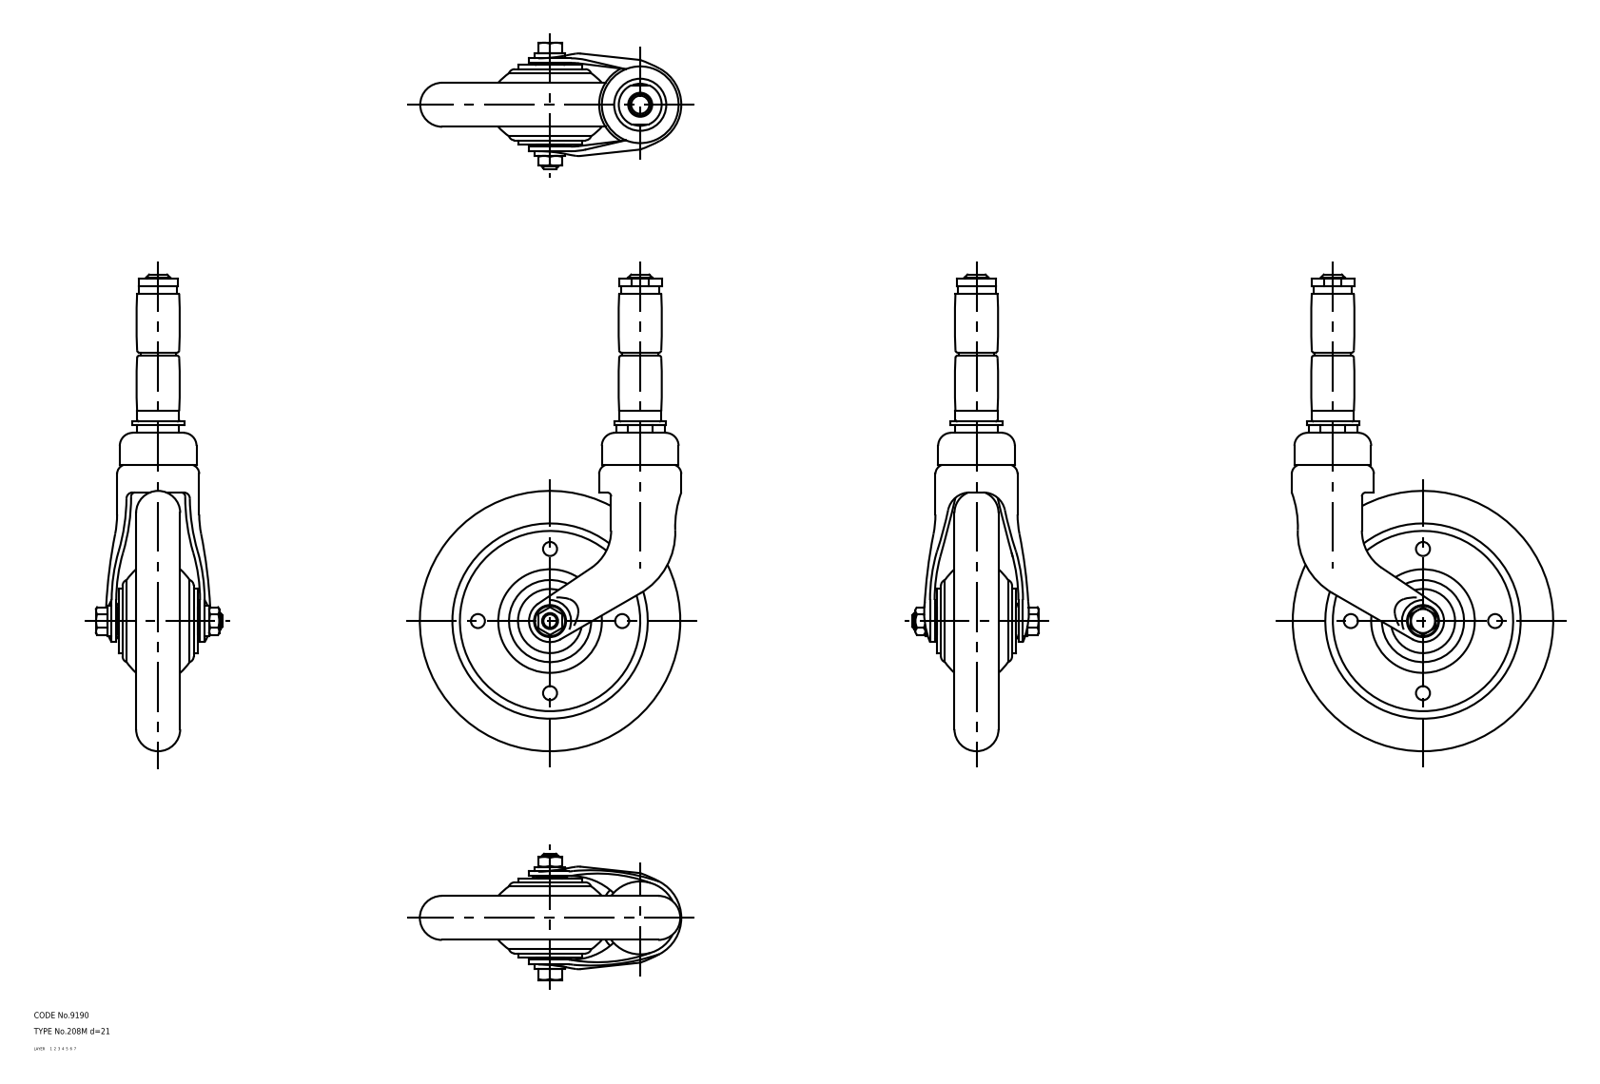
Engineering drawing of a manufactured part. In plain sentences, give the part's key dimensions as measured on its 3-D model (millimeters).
The part is named "wheel; main shaft; axle; No_208M_d21_22356_36". Its 3-D file was written by "CADfix (AUTOMOTIVE_DESIGN)". It is 4 solids with 308 faces: 0 planar, 0 cylindrical and 308 other. Overall it measures 238 by 130.76 by 63 millimeters. Its volume is 299 958 cubic millimeters and its surface area 70 977 square millimeters.
